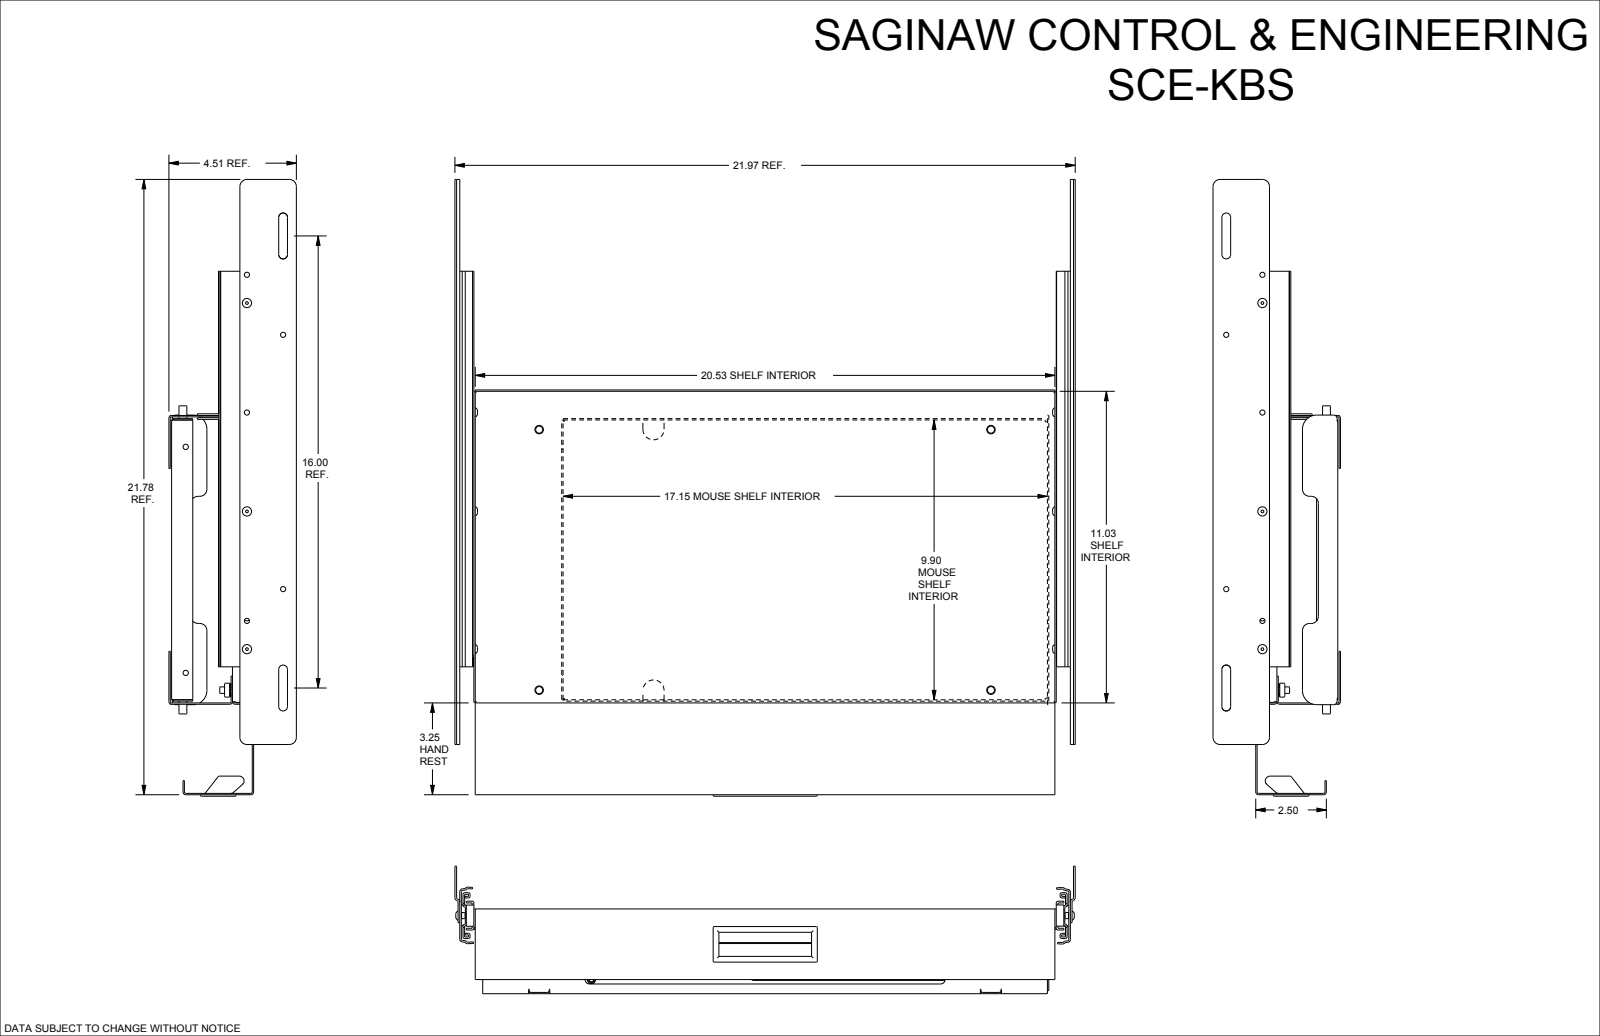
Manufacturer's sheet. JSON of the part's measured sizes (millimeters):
{"part_name": "SCE-KBS", "step_written_by": "SolidWorks 2019 (AUTOMOTIVE_DESIGN)", "units": "millimeters", "bodies": {"solids": 32, "faces": 956, "planar": 485, "cylindrical": 397, "other": 74}, "overall_size": [558, 554.5, 114.7], "volume_mm3": 1257000, "surface_area_mm2": 1505000, "round_holes": [[5.1, 22], [4.6, 8], [2.5, 6], [4, 6], [6.4, 4], [7.9, 4], [4.7, 2], [4, 1], [7.1, 1], [22.2, 1], [22.2, 1]], "round_bosses_or_shafts": [[5.5, 6], [4.1, 6], [7.6, 4], [5.8, 4], [7.1, 1]], "partial_cylinders_radius": [[0.8, 20], [1.6, 16], [6.4, 16], [0.8, 15], [2.4, 11], [1.2, 10], [1.5, 9], [0.2, 8]], "face_to_face_distances": [1.2, 1.3, 54.7, 53.5, 54.7, 56, 2.4, 17.8, 57.2, 7.6], "hole_center_spacings": [25.4, 12.7, 273.1, 260.4, 285.8, 25.3, 311.2, 73]}
